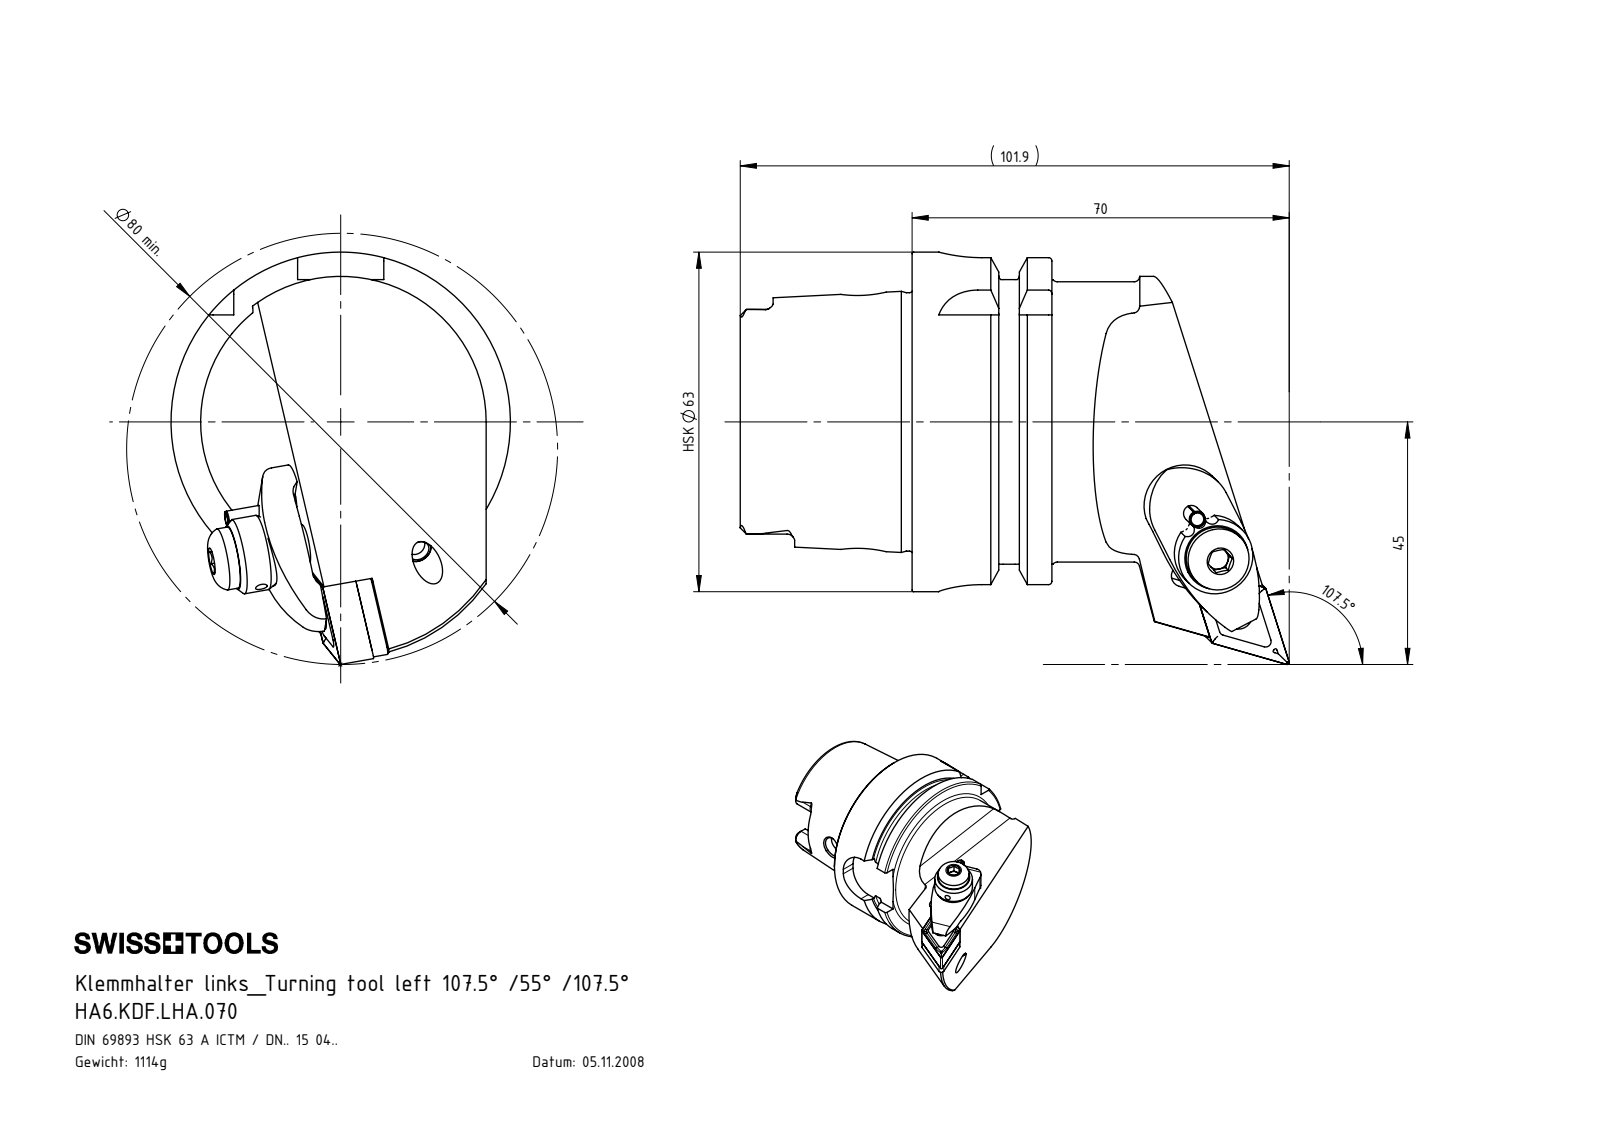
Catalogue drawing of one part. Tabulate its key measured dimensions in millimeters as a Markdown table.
| quantity | value |
| --- | --- |
| part name | DNMG150604; WCC-ER2.001.010_A; WDF-ER2.101.003_A; HA6-KDF.LHA.070_C (+7 more) |
| STEP written by | SolidWorks 2017 (AUTOMOTIVE_DESIGN) |
| units | millimeters |
| bodies | 11 solids, 463 faces (123 planar, 152 cylindrical, 188 other) |
| overall size | 101.9 × 76.5 × 63 |
| volume | 142 865 mm³ |
| surface area | 34 769 mm² |
| round holes (diameter × count) | 2 × 3, 4.2 × 2, 5 × 2, 7 × 2, 2.4 × 1, 3 × 1, 4 × 1, 5.16 × 1, 6.2 × 1, 6.4 × 1, 7.5 × 1, 8.4 × 1 |
| round bosses / shafts (diameter × count) | 5 × 2, 3 × 2, 63 × 1, 54.95 × 1, 52 × 1, 47.94 × 1, 14 × 1, 11.5 × 1 |
| partial cylindrical surfaces (radius × count) | 0.39 × 6, 1.4 × 6, 0.4 × 4, 1 × 4, 8 × 4, 0.69 × 3, 0.69 × 3, 1.5 × 3 |
| main face-to-face distances | 25.95, 16, 9.95, 31.9, 41.85, 57.85, 12.7, 6.05, 52.8, 3.18 |
| hole center spacings | 15, 23, 7.99, 8, 8.19, 14.81, 22.99 |
